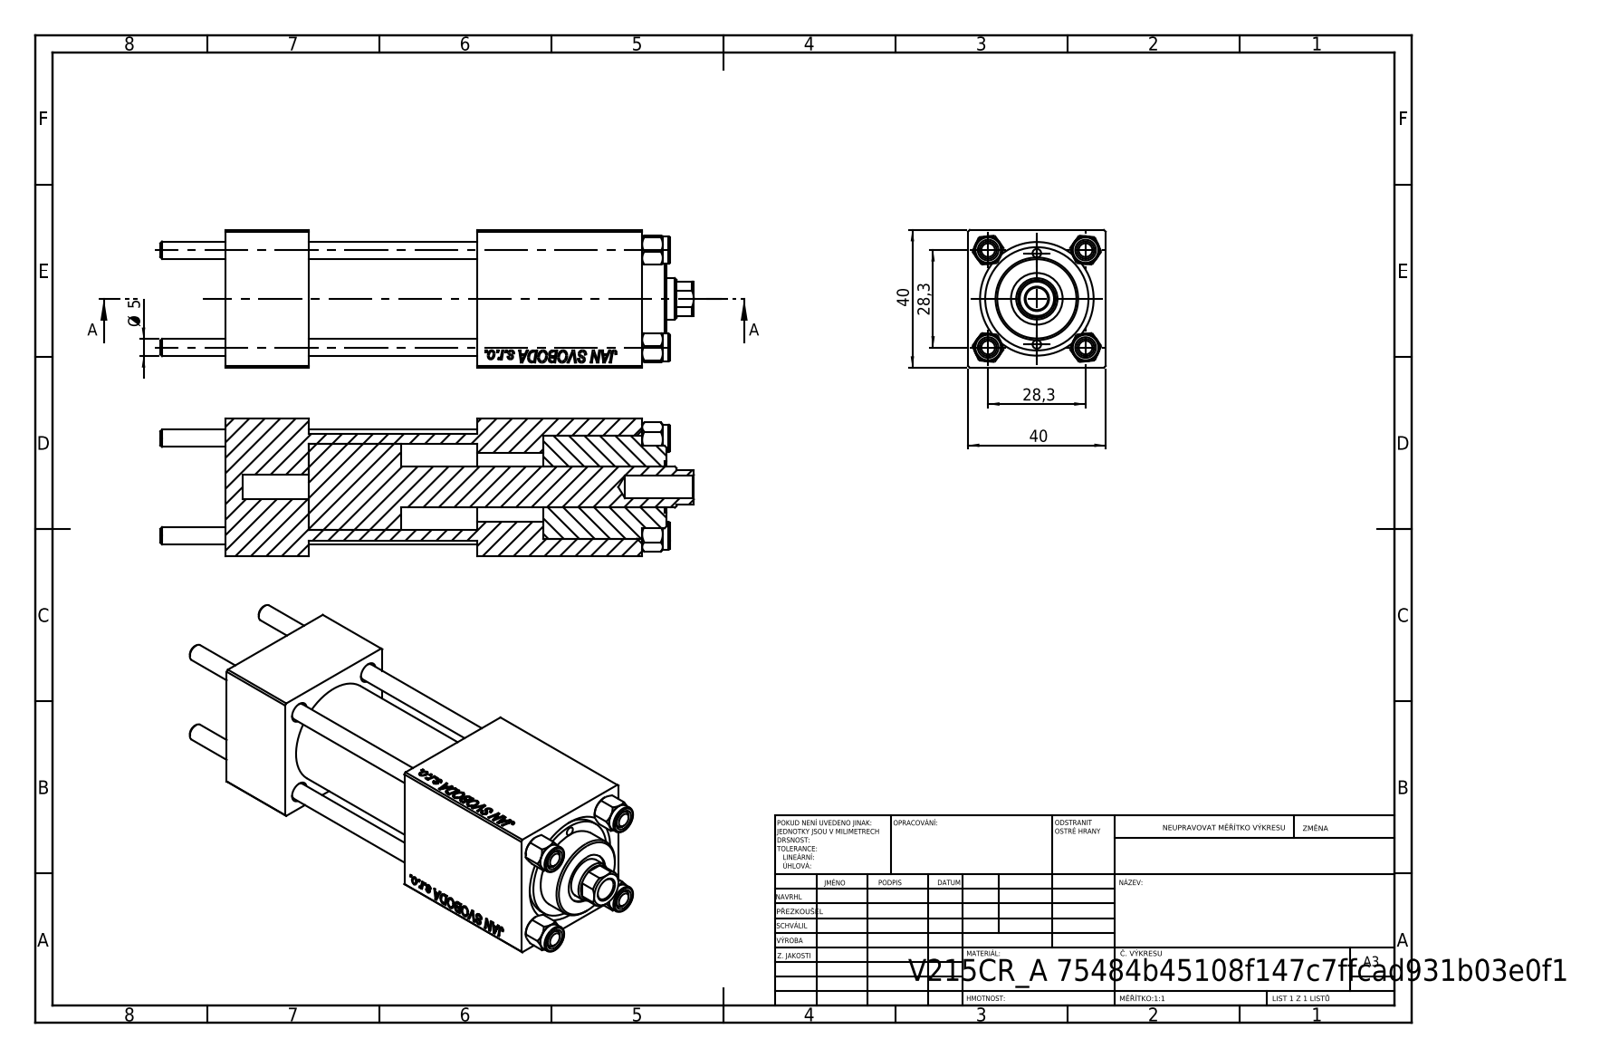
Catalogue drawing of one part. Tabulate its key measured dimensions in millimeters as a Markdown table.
| quantity | value |
| --- | --- |
| part name | NUT_M5; V215CR_VCP; CR025_012_A_0_G_A_G_M_020_+#_##_TYCINKA; V215CR_BODY_A (+1 more) |
| STEP written by | SolidWorks 2019 (CONFIG_CONTROL_DESIGN) |
| units | millimeters |
| bodies | 11 solids, 1137 faces (519 planar, 82 cylindrical, 536 other) |
| overall size | 155 × 40 × 40 |
| volume | 145 686 mm³ |
| surface area | 59 503 mm² |
| round holes (diameter × count) | 5 × 4, 20 × 3, 2.5 × 2, 7 × 2, 13.16 × 2, 6.5 × 1, 12 × 1, 15 × 1, 25 × 1, 30 × 1 |
| round bosses / shafts (diameter × count) | 8 × 4, 31 × 1, 24 × 1 |
| partial cylindrical surfaces (radius × count) | 5.5 × 1 |
| main face-to-face distances | 40, 24, 92.3, 68.3, 121, 97, 28.7, 73, 49, 19.3 |
| hole center spacings | 14.18, 20.01, 28.3, 30.84, 13.25, 40.02, 26.5, 74 |
